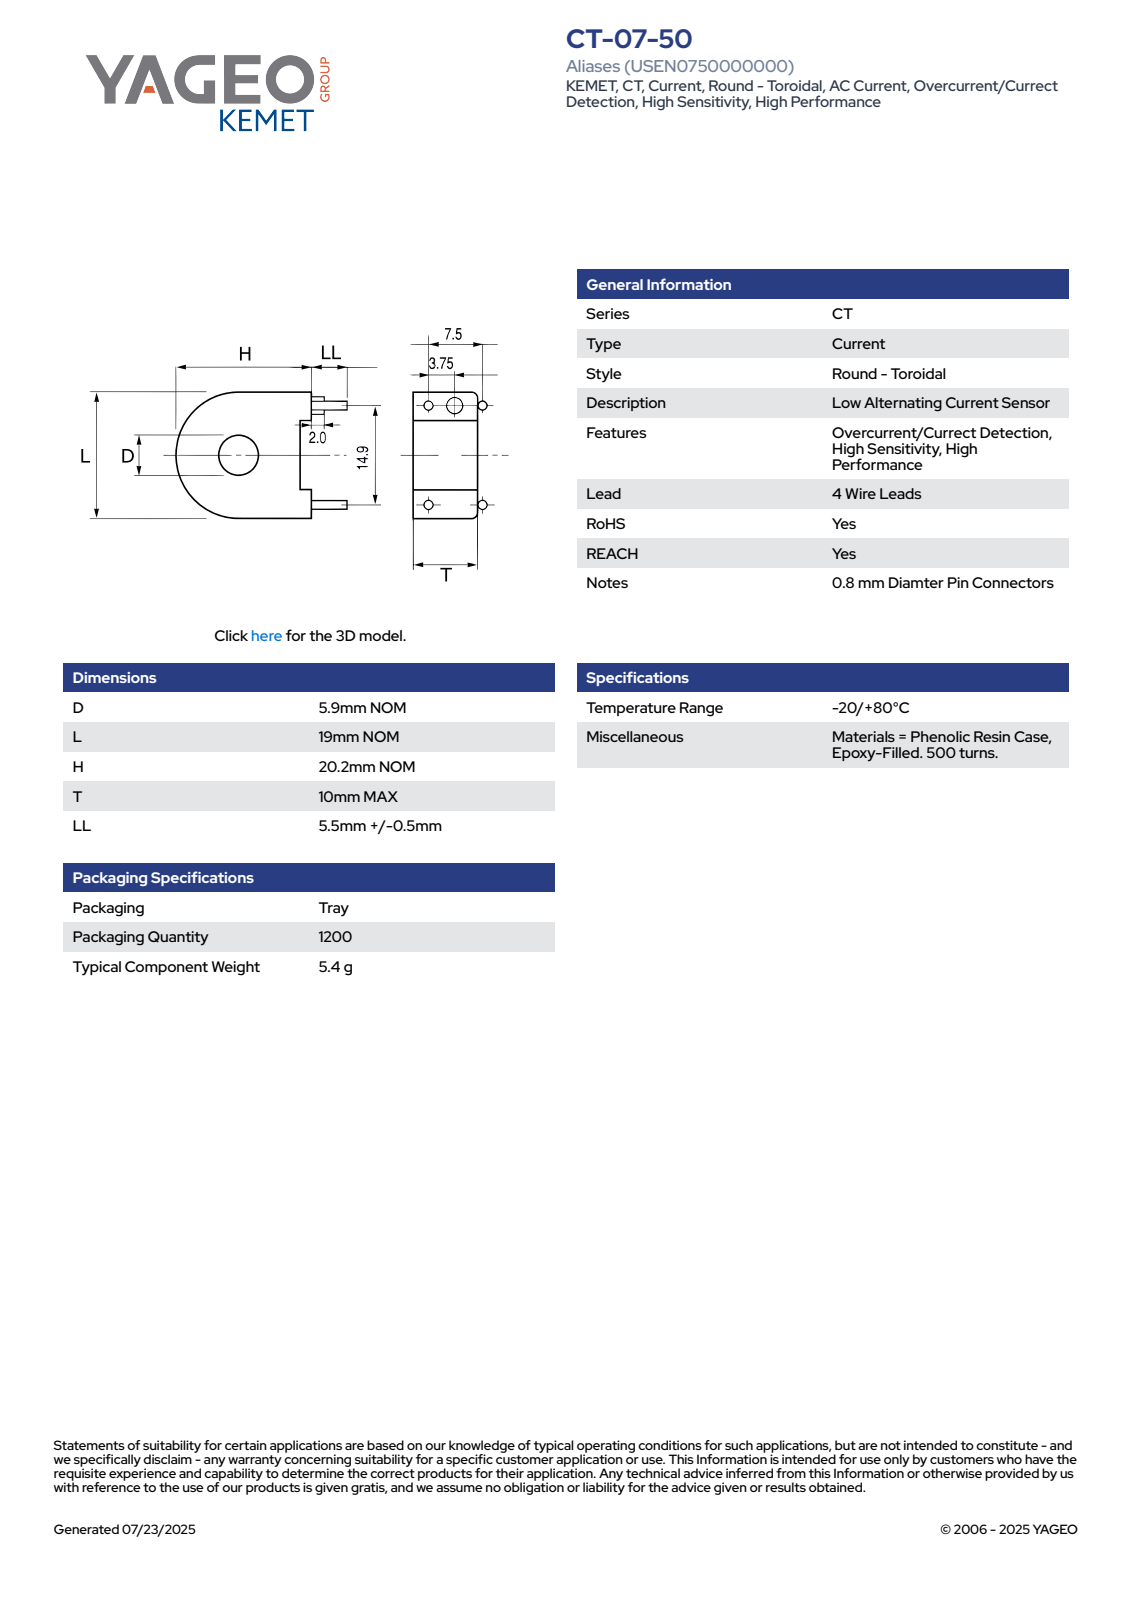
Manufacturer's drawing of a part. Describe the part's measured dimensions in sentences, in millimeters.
The part is named "Default". Its 3-D file was written by "SolidWorks 2014 (AUTOMOTIVE_DESIGN)". It is 1 solid with 90 faces: 36 planar, 20 cylindrical and 34 other. Overall it measures 26.2 by 19 by 10.96 millimeters. Its volume is 3 123 cubic millimeters and its surface area 1 631 square millimeters. Round holes: 1 of diameter 5.9. Round bosses or shafts: 4 of diameter 1, 1 of diameter 1.81. Partial cylindrical surfaces (rounded edges, fillets, slot ends): 2 of radius 0.75, 1 of radius 9.49, 1 of radius 9.5. The main face-to-face distances are 10, 19, 0.81, 4.32, 14.68, 10.36, 6, 6.81, 4, 2.81.
